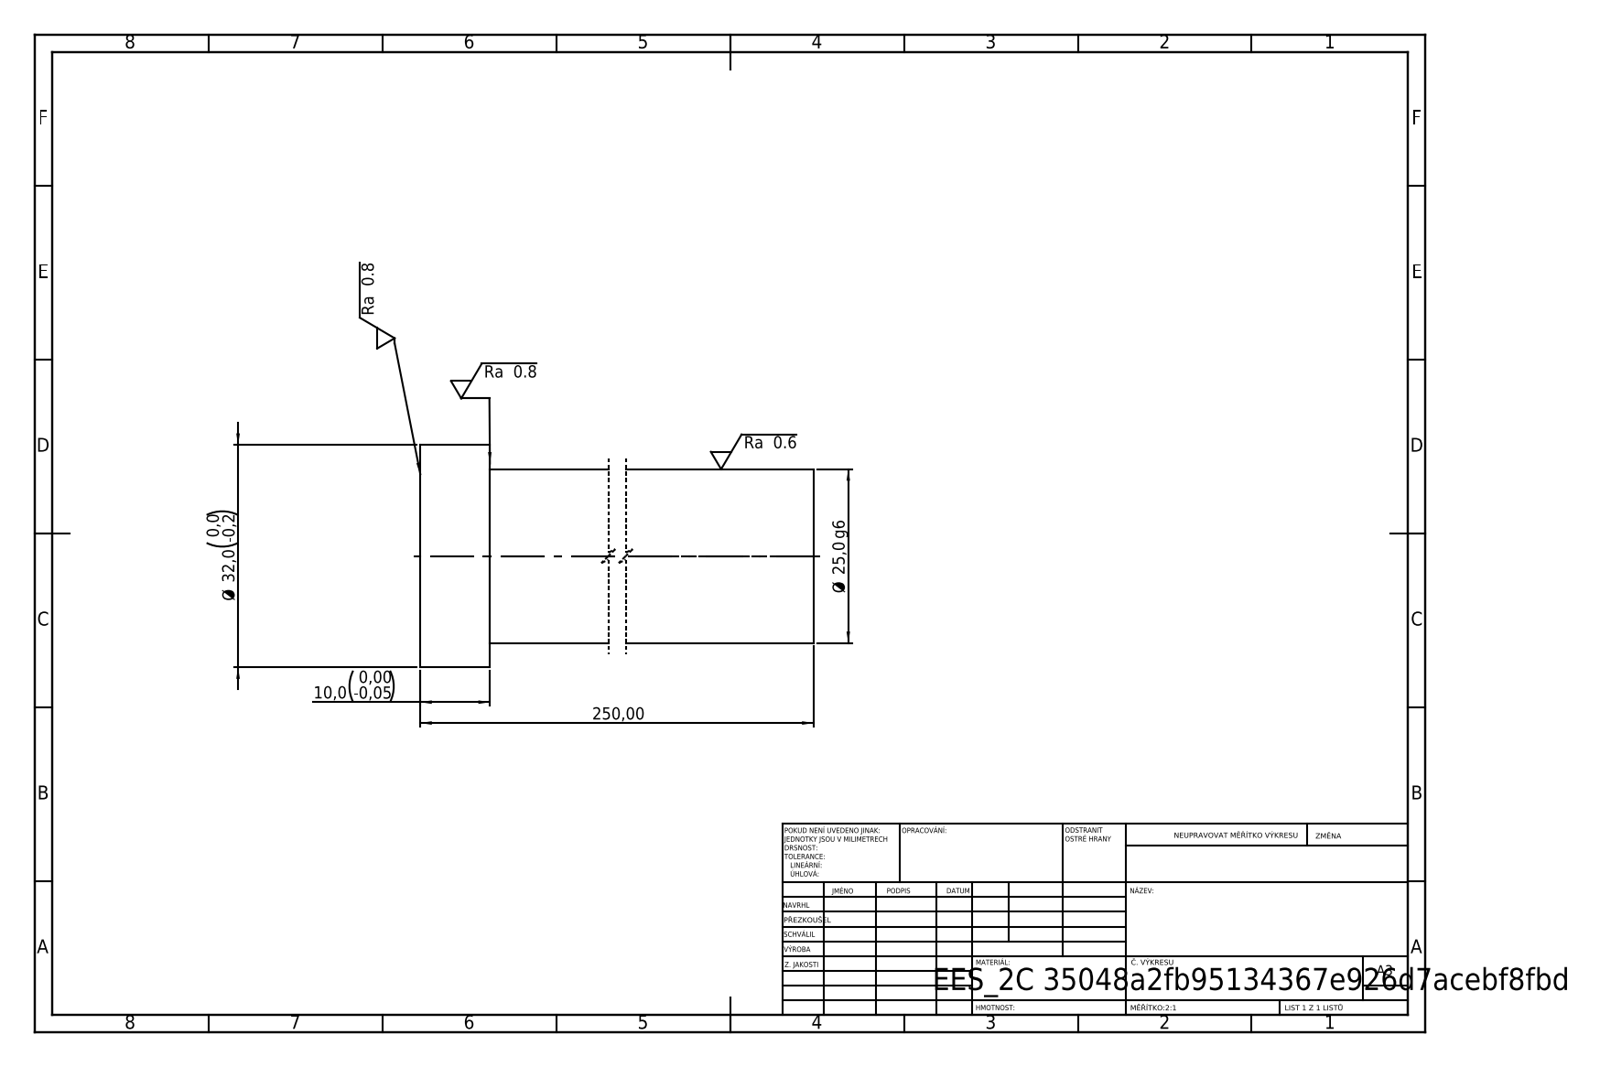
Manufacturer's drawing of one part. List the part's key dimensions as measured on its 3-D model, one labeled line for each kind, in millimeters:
STEP written by: SolidWorks 2019 (CONFIG_CONTROL_DESIGN)
Units: millimetres
Bodies: 1 solid, 7 faces (3 planar, 4 cylindrical, 0 other)
Overall size (bounding box): 250 × 32 × 32
Volume: 125 852 mm³ · Surface area: 21 463 mm²
Round bosses / shafts (diameter × count): ⌀32 ×1, ⌀25 ×1
Main face-to-face distances: 250, 10, 240
